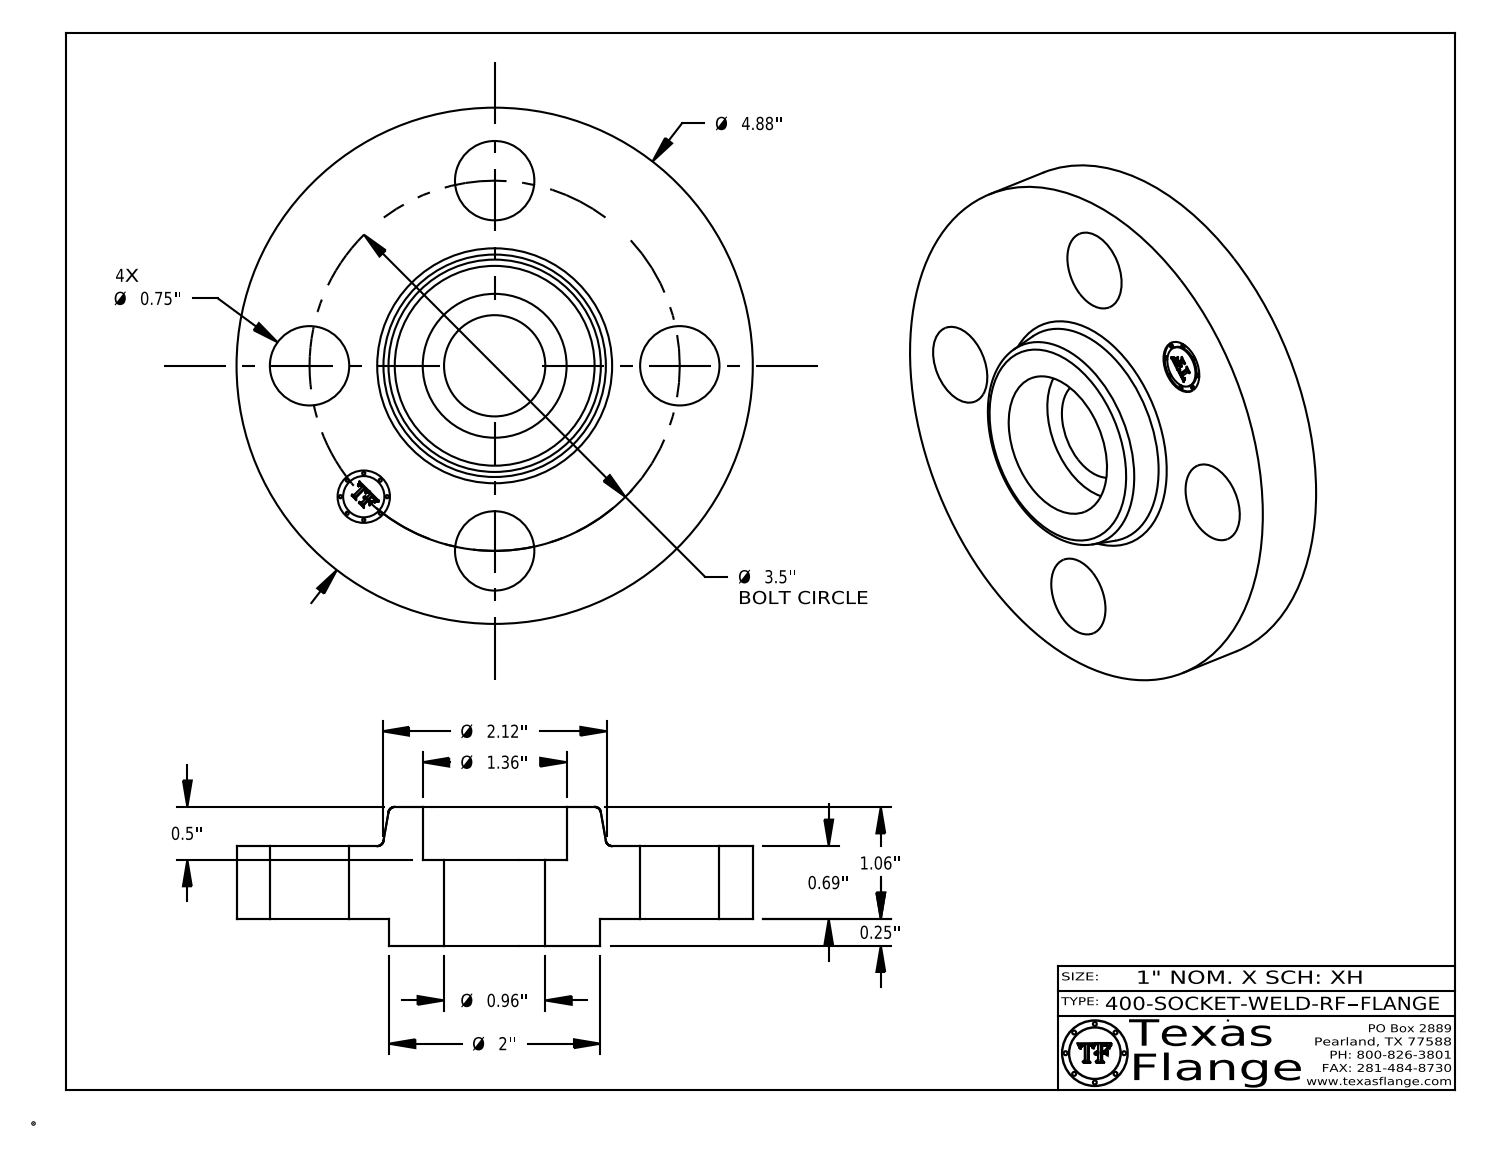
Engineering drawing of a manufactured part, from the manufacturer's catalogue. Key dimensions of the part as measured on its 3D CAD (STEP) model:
Part name (STEP PRODUCT): 400-SOCKET-WELD-RF
STEP written by: CATIA V5 STEP AP214 (AUTOMOTIVE_DESIGN)
Units: inches
Bodies: 1 solid, 412 faces (370 planar, 36 cylindrical, 6 other)
Overall size (bounding box): 4.88 × 4.88 × 1.31
Volume: 12.39 in³ · Surface area: 57.54 in²
Round holes (diameter × count): ⌀0.75 ×4, ⌀0.495 ×1, ⌀0.957 ×1, ⌀1.36 ×1
Round bosses / shafts (diameter × count): ⌀0.03 ×8, ⌀4.88 ×1, ⌀2 ×1, ⌀0.39 ×1
Main face-to-face distances: 0.69, 0.25, 0.94, 1.31, 1.06, 0.37, 0.81, 0.56, 0.13, 0.5
Hole centre spacings: 1.75, 2.475, 1.339, 3.233, 3.5
